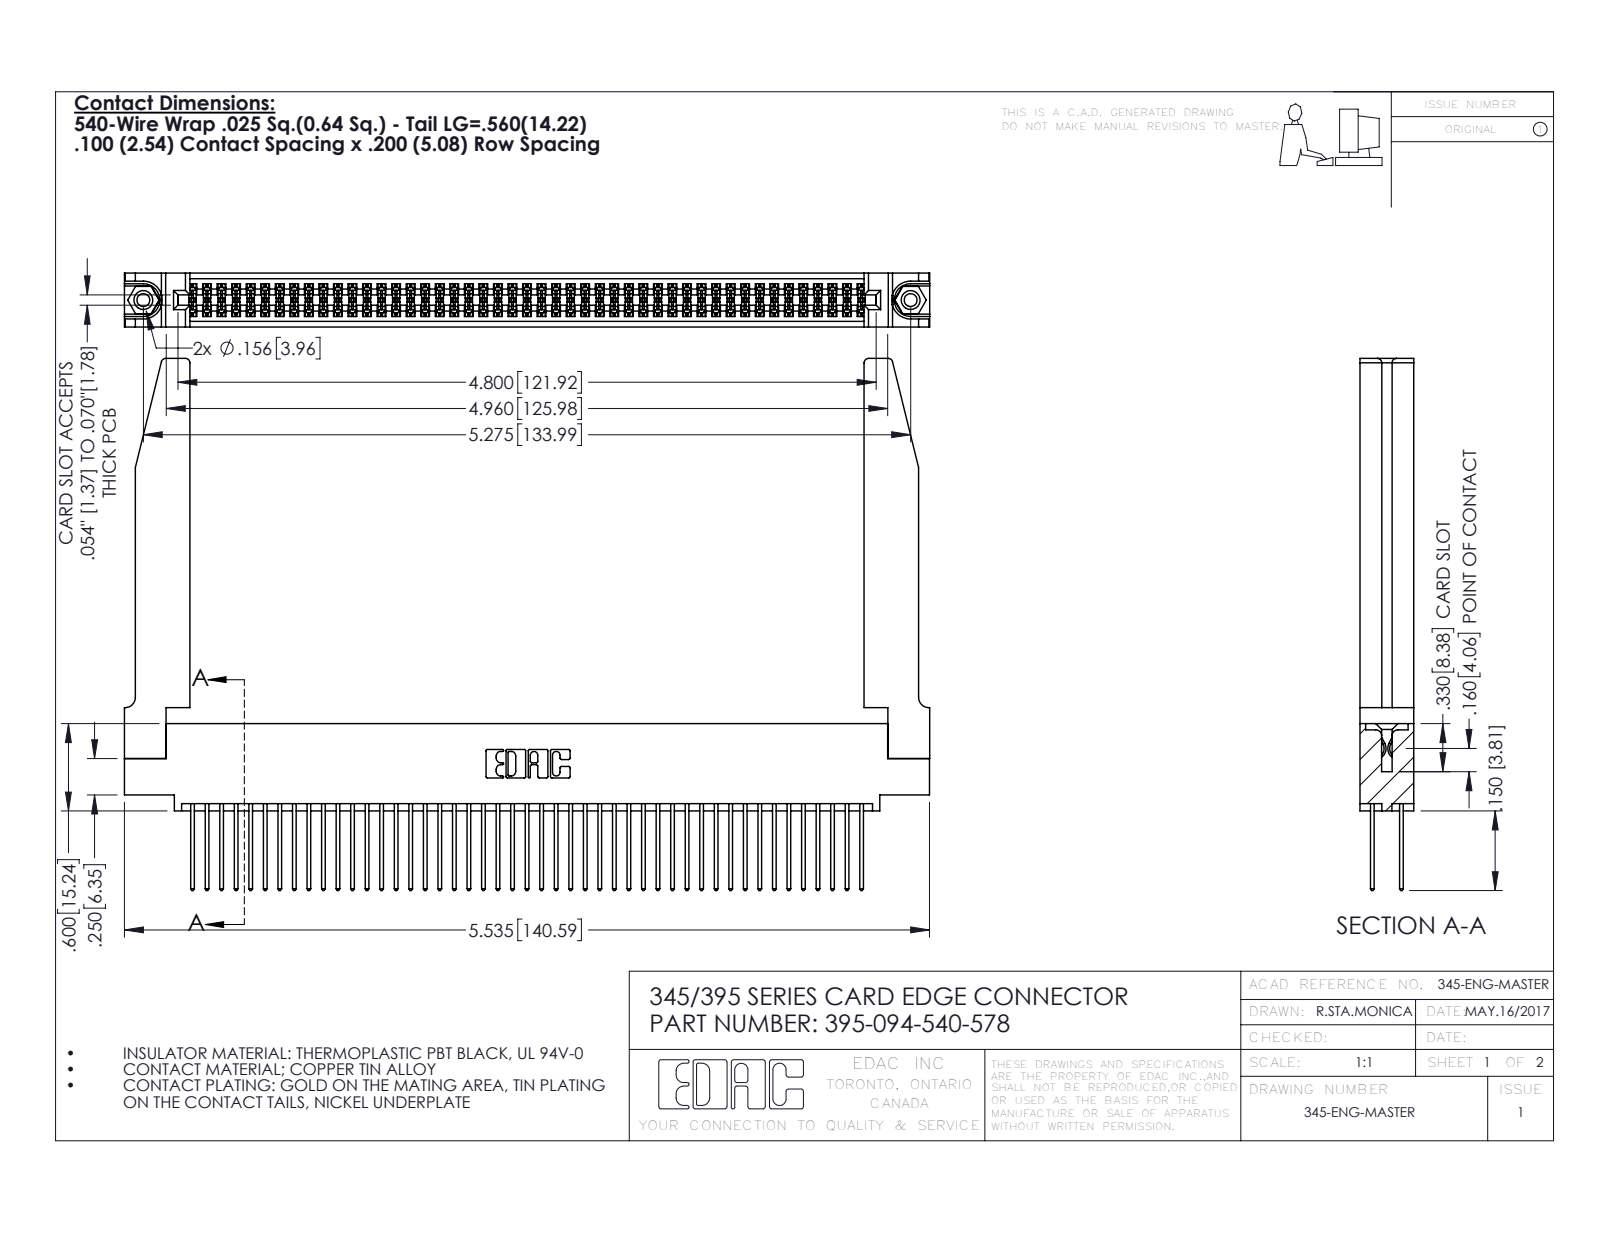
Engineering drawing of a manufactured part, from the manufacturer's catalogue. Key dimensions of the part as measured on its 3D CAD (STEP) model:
Part name (STEP PRODUCT): 345-220-078_345-220-078; 395-094-540-578; 345 Part_0.110 Offset - 0.156 Dia-TH; 345-292-001_345-293-140 (+1 more)
STEP written by: SolidWorks 2016 (CONFIG_CONTROL_DESIGN)
Units: inches
Bodies: 99 solids, 5064 faces (3328 planar, 1684 cylindrical, 52 other)
Overall size (bounding box): 5.536 × 3.657 × 0.37
Volume: 1.328 in³ · Surface area: 45.51 in²
Round holes (diameter × count): ⌀0.089 ×2, ⌀0.125 ×2, ⌀0.156 ×2, ⌀0.064 ×1
Round bosses / shafts (diameter × count): ⌀0.155 ×2
Partial cylindrical surfaces — rounded edges, fillets, slot ends (radius × count): R0.006 ×141, R0.01 ×94, R0.01 ×22, R0.03 ×8, R0.007 ×6, R0.031 ×6, R0.026 ×3, R0.014 ×2
Main face-to-face distances: 0.072, 0.298, 0.37, 0.098, 0.272, 0.025, 0.2, 0.225, 0.175, 0.148
Hole centre spacings: 0.27, 5.039, 5.275
